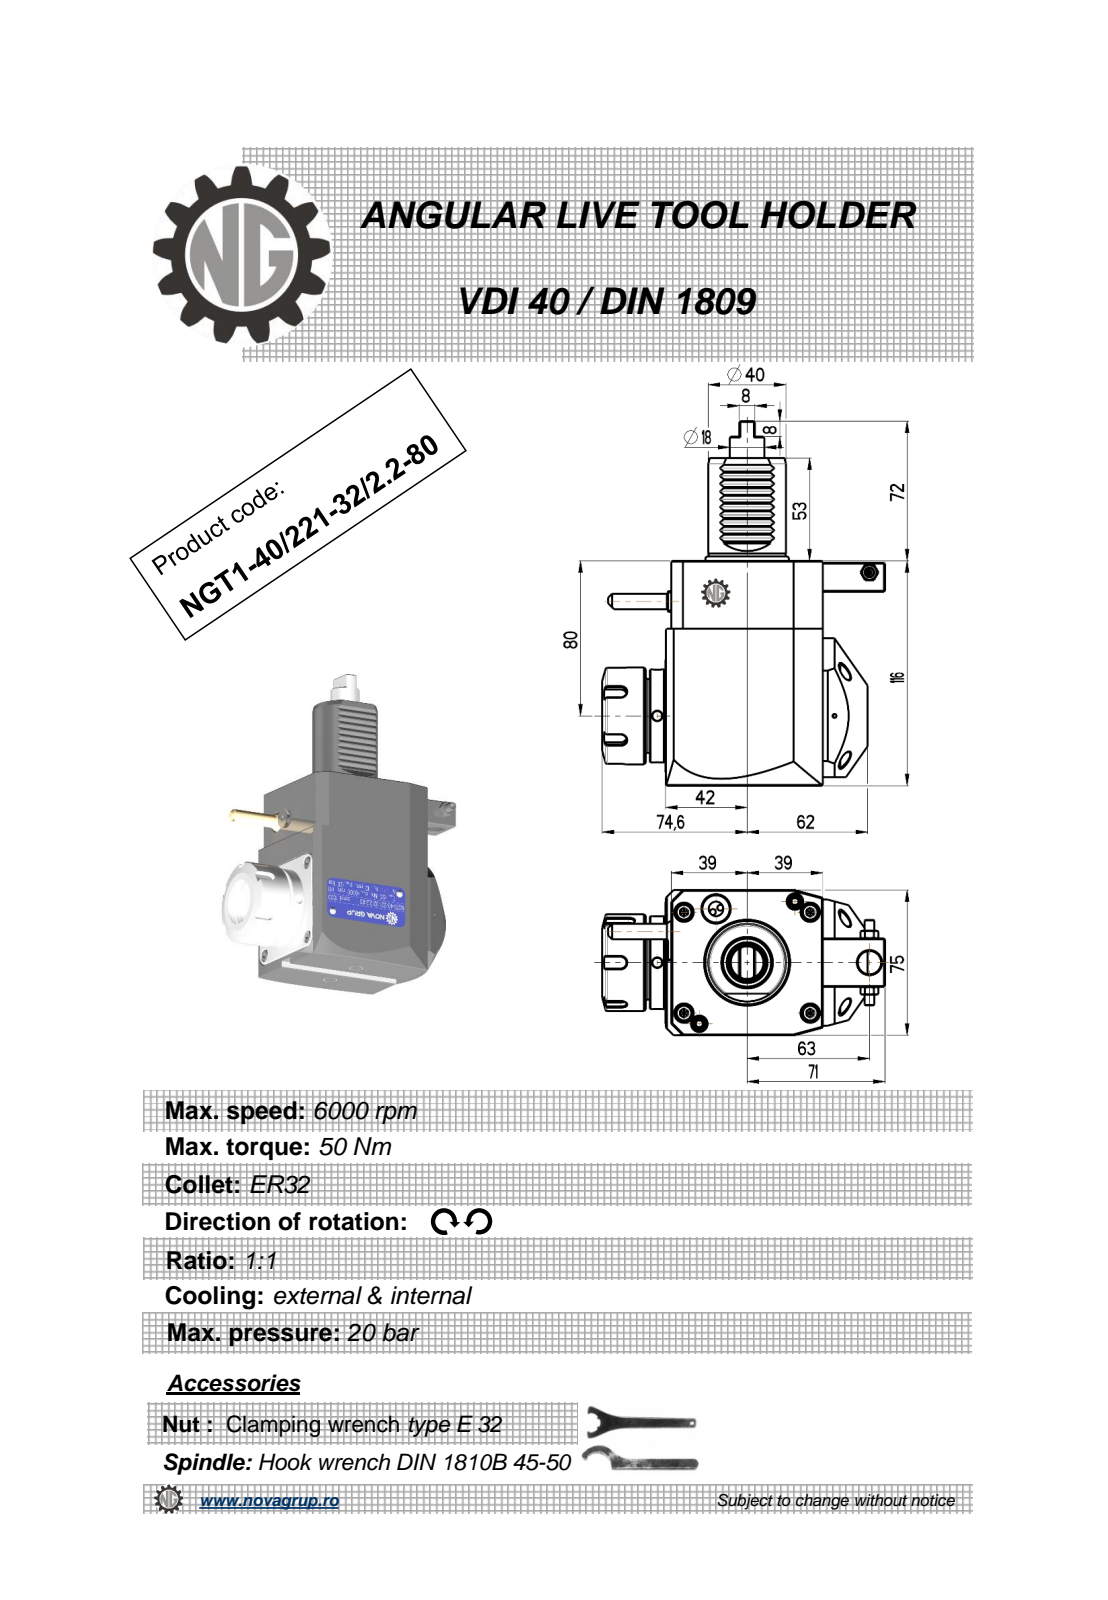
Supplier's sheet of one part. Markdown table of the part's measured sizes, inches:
| quantity | value |
| --- | --- |
| part name | NGT1_40_221_32_2_2_80 |
| STEP written by | PRO/ENGINEER BY PARAMETRIC TECHNOLOGY CORPORATION, 2010280 (CONFIG_CONTROL_DESIGN) |
| units | inches |
| bodies | 1 solid, 409 faces (193 planar, 89 cylindrical, 127 other) |
| overall size | 7.402 × 5.732 × 3.016 |
| volume | 53.89 in³ |
| surface area | 109 in² |
| round holes (diameter × count) | 0.197 × 3, 0.118 × 1, 0.165 × 1, 0.374 × 1, 0.472 × 1, 1.063 × 1 |
| round bosses / shafts (diameter × count) | 1.969 × 1, 1.89 × 1, 1.614 × 1, 1.575 × 1, 0.701 × 1, 0.441 × 1, 0.353 × 1, 0.315 × 1 |
| partial cylindrical surfaces (radius × count) | 0.01 × 12, 0.012 × 10, 0.009 × 6, 0.118 × 5, 0.031 × 2, 0.02 × 1, 1.575 × 1 |
| main face-to-face distances | 2.953, 4.567, 3.189, 0.118, 3.071, 0.11, 3.181, 4.409, 0.984, 0.295 |
| hole center spacings | 0.824, 2.407, 2.854, 4.301, 5.195 |
